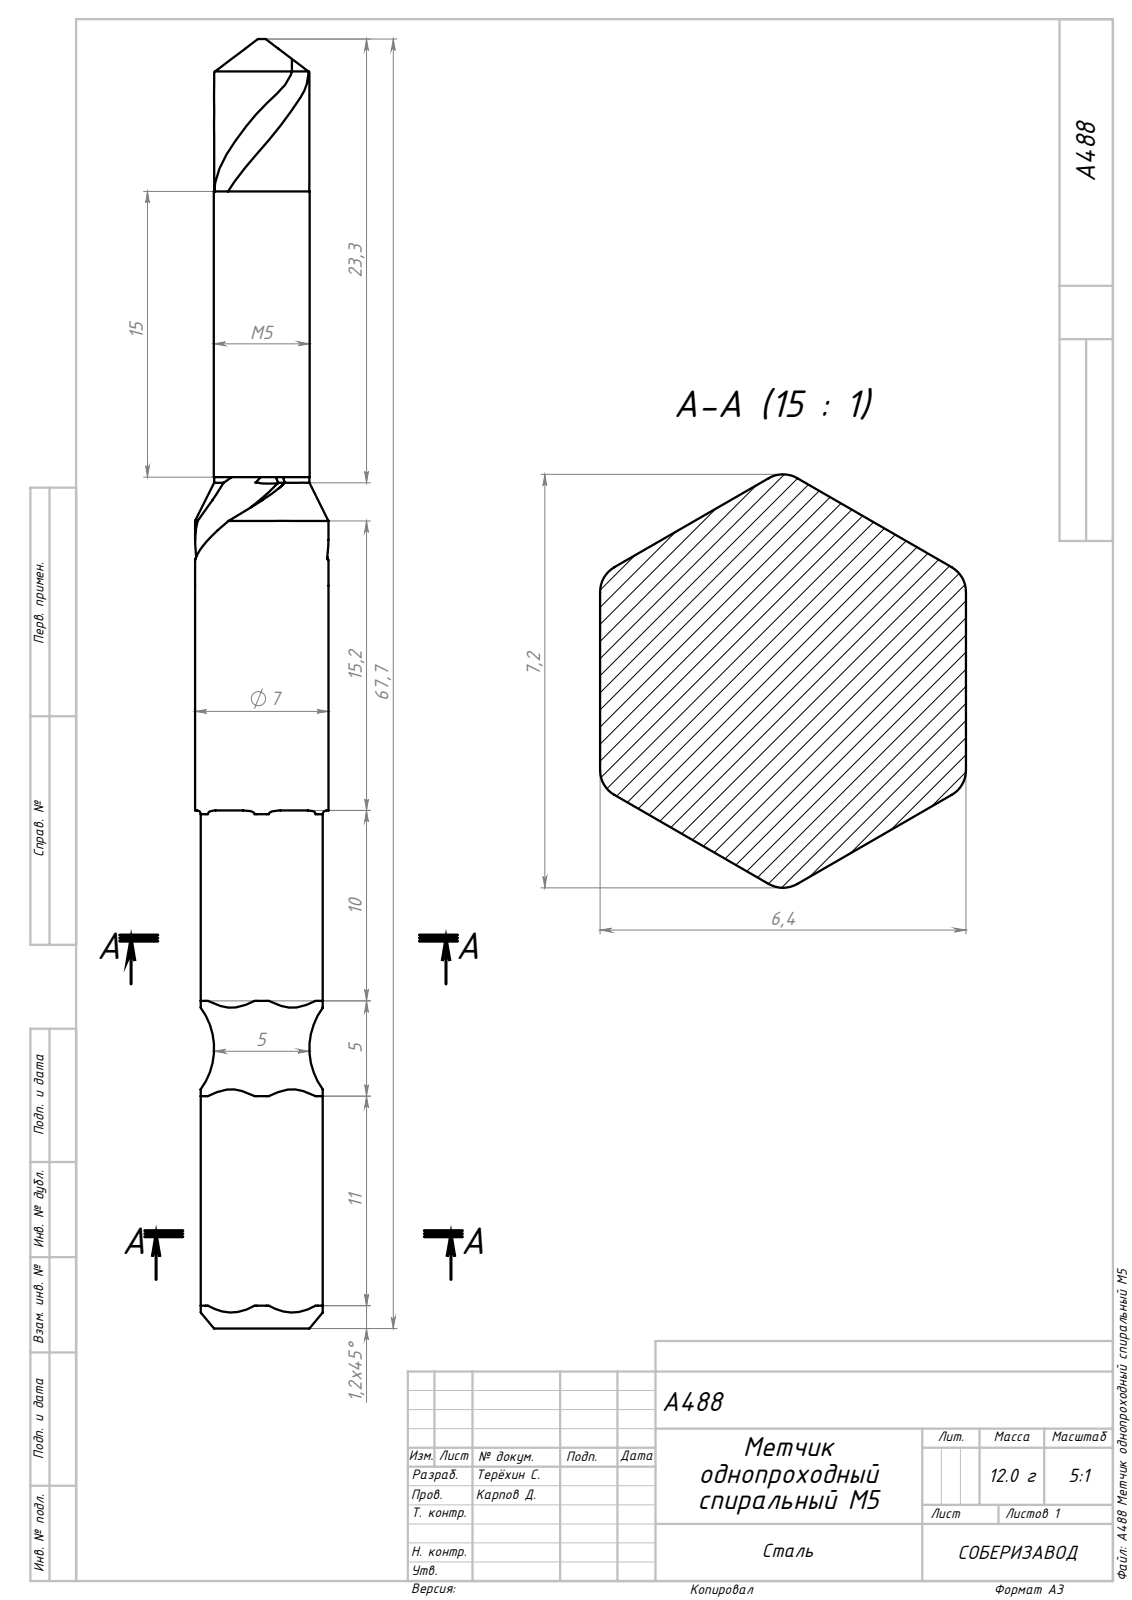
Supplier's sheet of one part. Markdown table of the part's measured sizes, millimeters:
| quantity | value |
| --- | --- |
| part name | A488 Метчик однопроходный спиральный М5 |
| STEP written by | SolidWorks 2021 (AUTOMOTIVE_DESIGN) |
| units | millimeters |
| bodies | 1 solid, 121 faces (48 planar, 31 cylindrical, 42 other) |
| overall size | 67.7 × 7.24 × 7 |
| volume | 1 957 mm³ |
| surface area | 1 390 mm² |
| round holes (diameter × count) | 2 × 1 |
| round bosses / shafts (diameter × count) | 7 × 1, 5.03 × 1 |
| partial cylindrical surfaces (radius × count) | 0.2 × 6, 0.5 × 6, 0.9 × 2, 2.5 × 1 |
| main face-to-face distances | 6.4, 2.55, 3.7, 8.95, 10.1, 2.7, 3.85, 44.7, 15, 59.7 |
